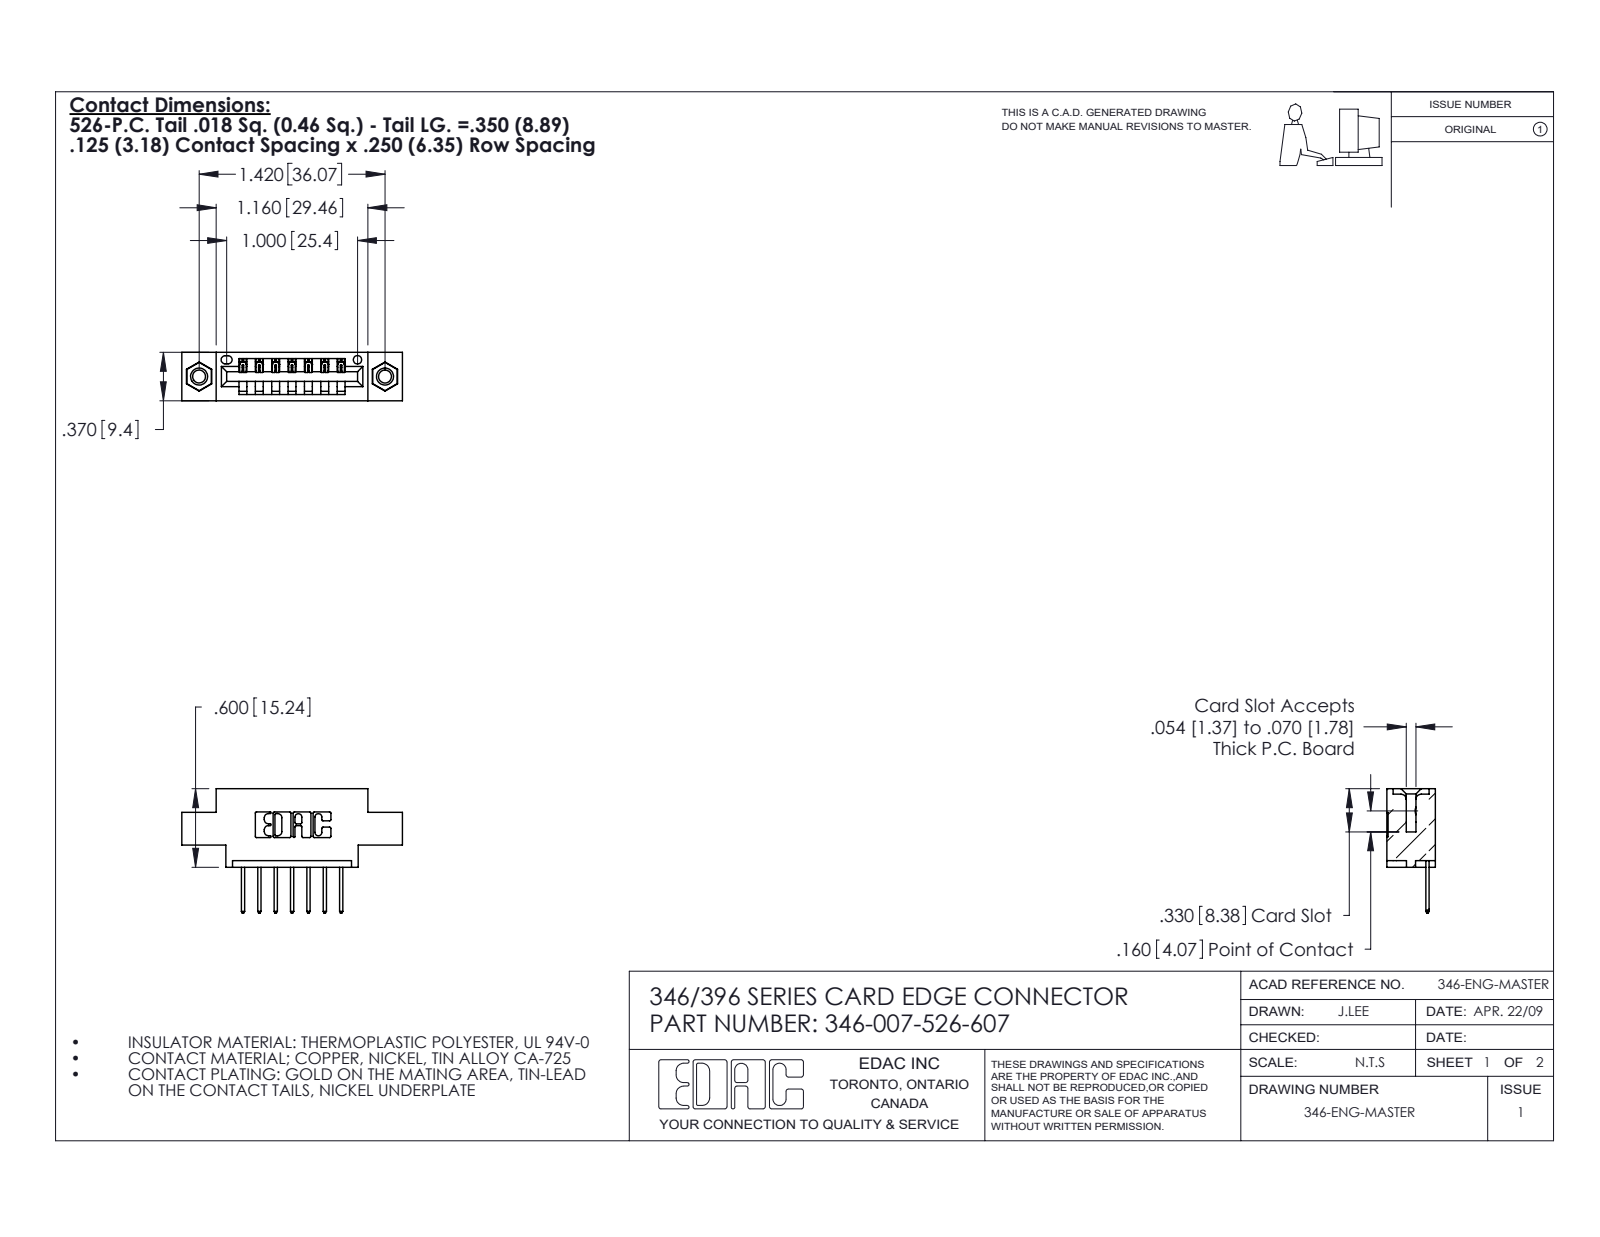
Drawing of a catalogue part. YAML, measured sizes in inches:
part_name: "346-007-526-607; 345-292-001_345-293-126; 346 Part_0.170 Offset - 0.156 Dia-TI; 345-250-001_345-250-005-103"
step_written_by: "SolidWorks 2020 (CONFIG_CONTROL_DESIGN)"
units: inches
bodies: {solids: 10, faces: 592, planar: 392, cylindrical: 184, other: 16}
overall_size: [1.685, 0.95, 0.37]
volume: 0.225
surface_area: 6.839
round_holes:
  - {diameter: 0.098, count: 2}
  - {diameter: 0.125, count: 2}
  - {diameter: 0.156, count: 2}
  - {diameter: 0.064, count: 1}
round_bosses_or_shafts:
  - {diameter: 0.155, count: 2}
partial_cylinders:
  - {radius: 0.01, count: 22}
  - {radius: 0.006, count: 14}
  - {radius: 0.01, count: 14}
  - {radius: 0.007, count: 6}
  - {radius: 0.031, count: 6}
  - {radius: 0.026, count: 3}
  - {radius: 0.031, count: 2}
  - {radius: 0.04, count: 2}
face_to_face_distances: [0.25, 0.37, 0.048, 0.322, 0.222, 0.148, 0.1, 0.174, 0.072, 0.298]
hole_center_spacings: [0.246, 1.217, 1.42]
